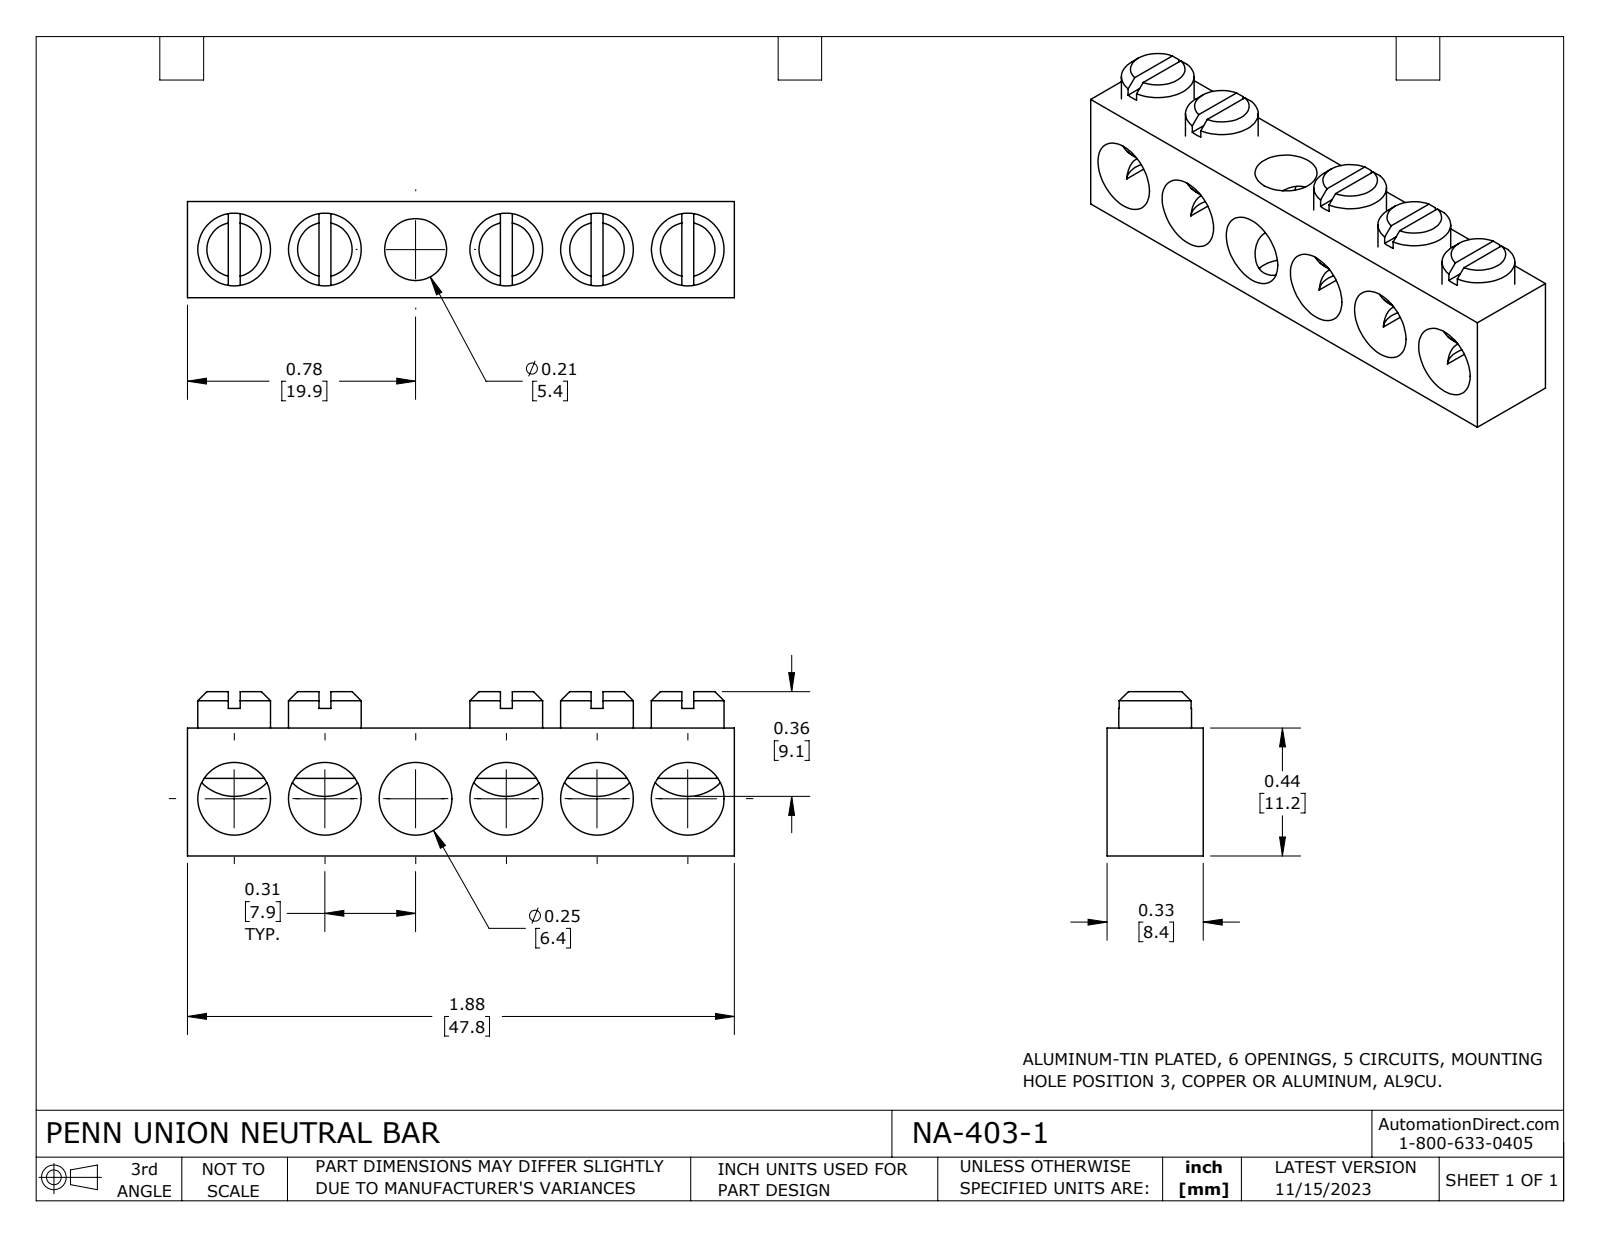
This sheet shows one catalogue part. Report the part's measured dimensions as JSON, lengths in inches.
{"part_name": "NA-403-1", "step_written_by": "SolidWorks 2023 (CONFIG_CONTROL_DESIGN)", "units": "inches", "bodies": {"solids": 6, "faces": 112, "planar": 41, "cylindrical": 46, "other": 25}, "overall_size": [1.88, 0.565, 0.331], "volume_in3": 0.222, "surface_area_in2": 6.053, "round_holes": [[0.213, 6], [0.25, 6]], "round_bosses_or_shafts": [[0.25, 5]], "face_to_face_distances": [0.331, 0.44, 1.88, 0.565, 0.125, 0.312, 0.041, 0.935, 1.247, 0.624], "hole_center_spacings": [0.312, 0.624, 0.935, 1.247, 1.559]}
